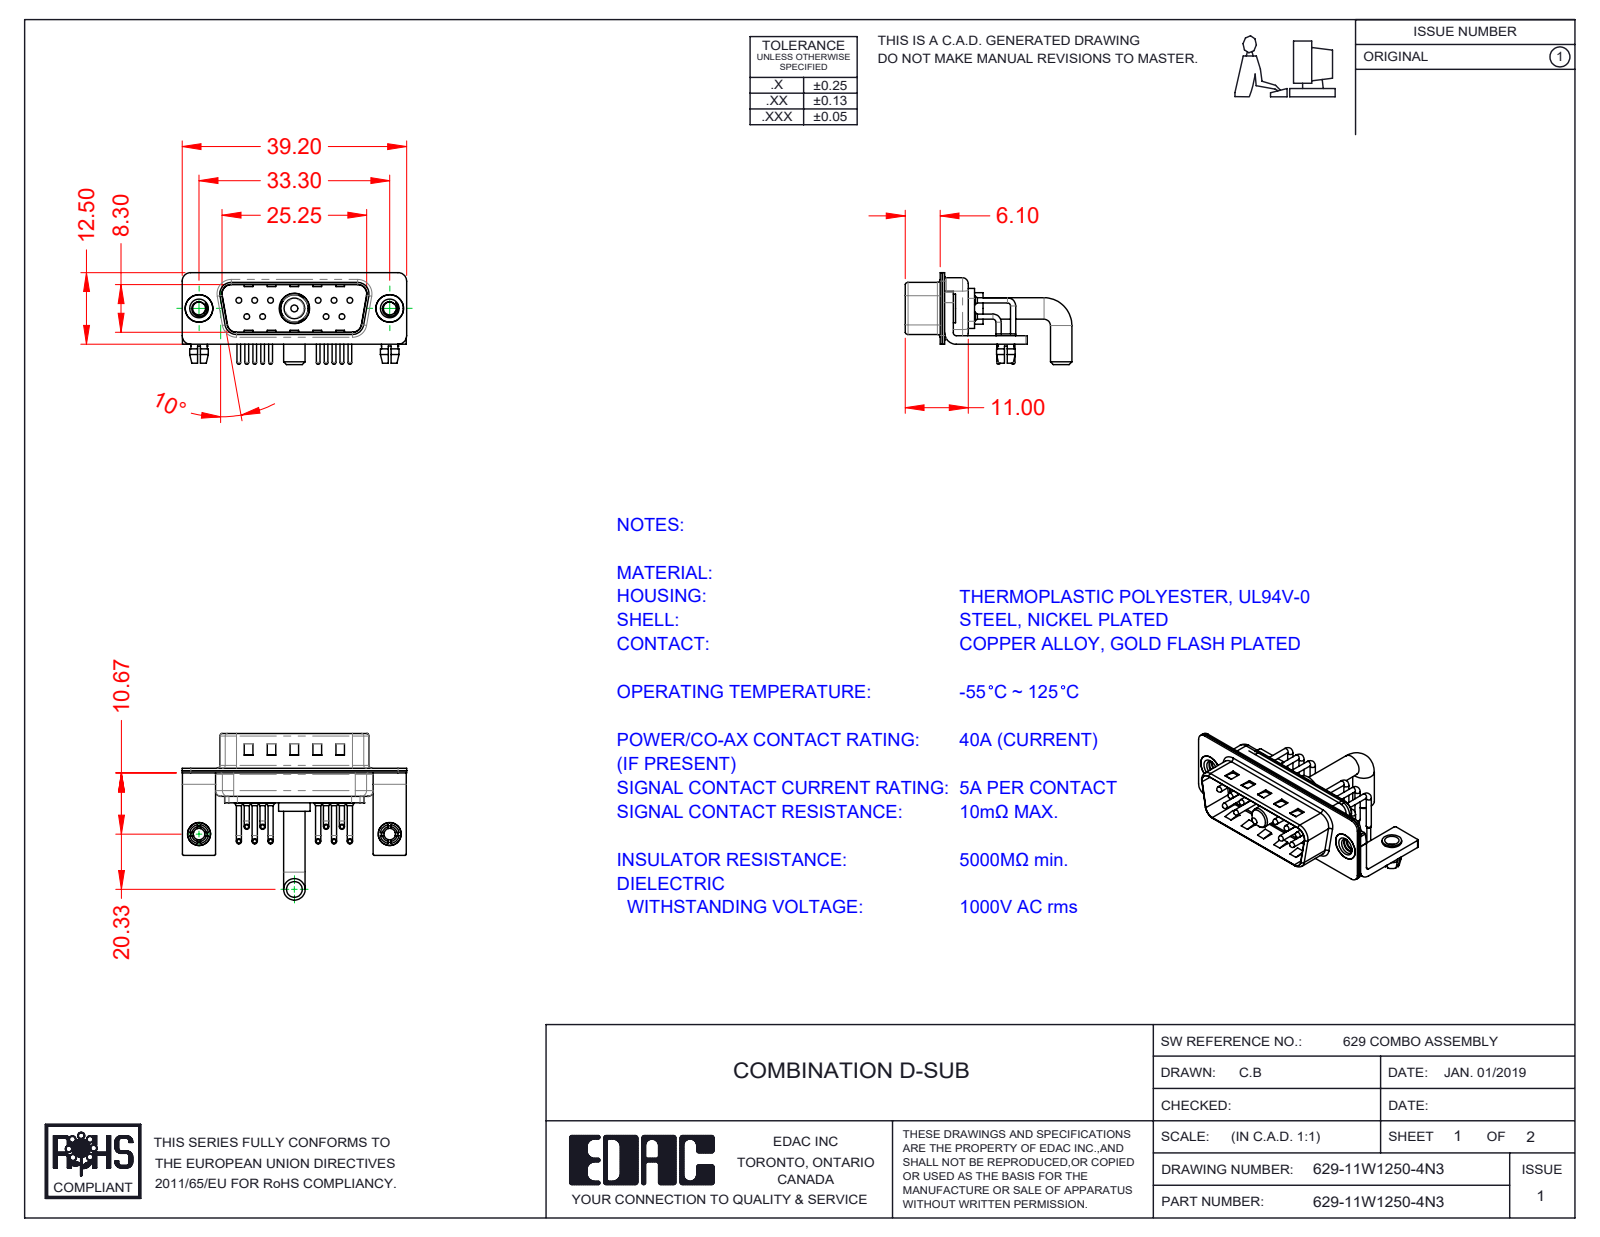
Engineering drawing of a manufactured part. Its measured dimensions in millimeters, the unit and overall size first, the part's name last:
Units: millimetres
Overall size (bounding box): 39.2 × 29.11 × 16.05
Round holes (diameter × count): ⌀2 ×12, ⌀0.75 ×10, ⌀1.6 ×10, ⌀2.26 ×2, ⌀2.5 ×2, ⌀3.2 ×2, ⌀4 ×2, ⌀4.8 ×2, ⌀4.85 ×1, ⌀5.3 ×1
Round bosses / shafts (diameter × count): ⌀0.9 ×20, ⌀1.5 ×10, ⌀1 ×10, ⌀0.65 ×10, ⌀5 ×2, ⌀4.9 ×2, ⌀4 ×2, ⌀3.75 ×2
Partial cylindrical surfaces — rounded edges, fillets, slot ends (radius × count): R0.25 ×16, R1.5 ×16, R2 ×13, R1.01 ×10, R0.5 ×9, R1.6 ×8, R1 ×7, R0.6 ×4
Main face-to-face distances: 0.4, 0.8, 1.5, 9.5, 9.1, 8.7, 9.9, 0.6, 1.9, 2.1
Hole centre spacings: 3.16, 2.77, 13.85, 11.08, 16.62, 5.03, 5.04, 5.54
Volume: 2 519 mm³ · Surface area: 6 158 mm²
Bodies: 21 solids, 1628 faces (866 planar, 568 cylindrical, 194 other)
Part name (STEP PRODUCT): 629Combo Shell Front_15 Contacts; 629Combo Housing_11W1; 629-11W1250-4N3; 629Combo Board Lock (+6 more)
STEP written by: SolidWorks 2020 (CONFIG_CONTROL_DESIGN)
